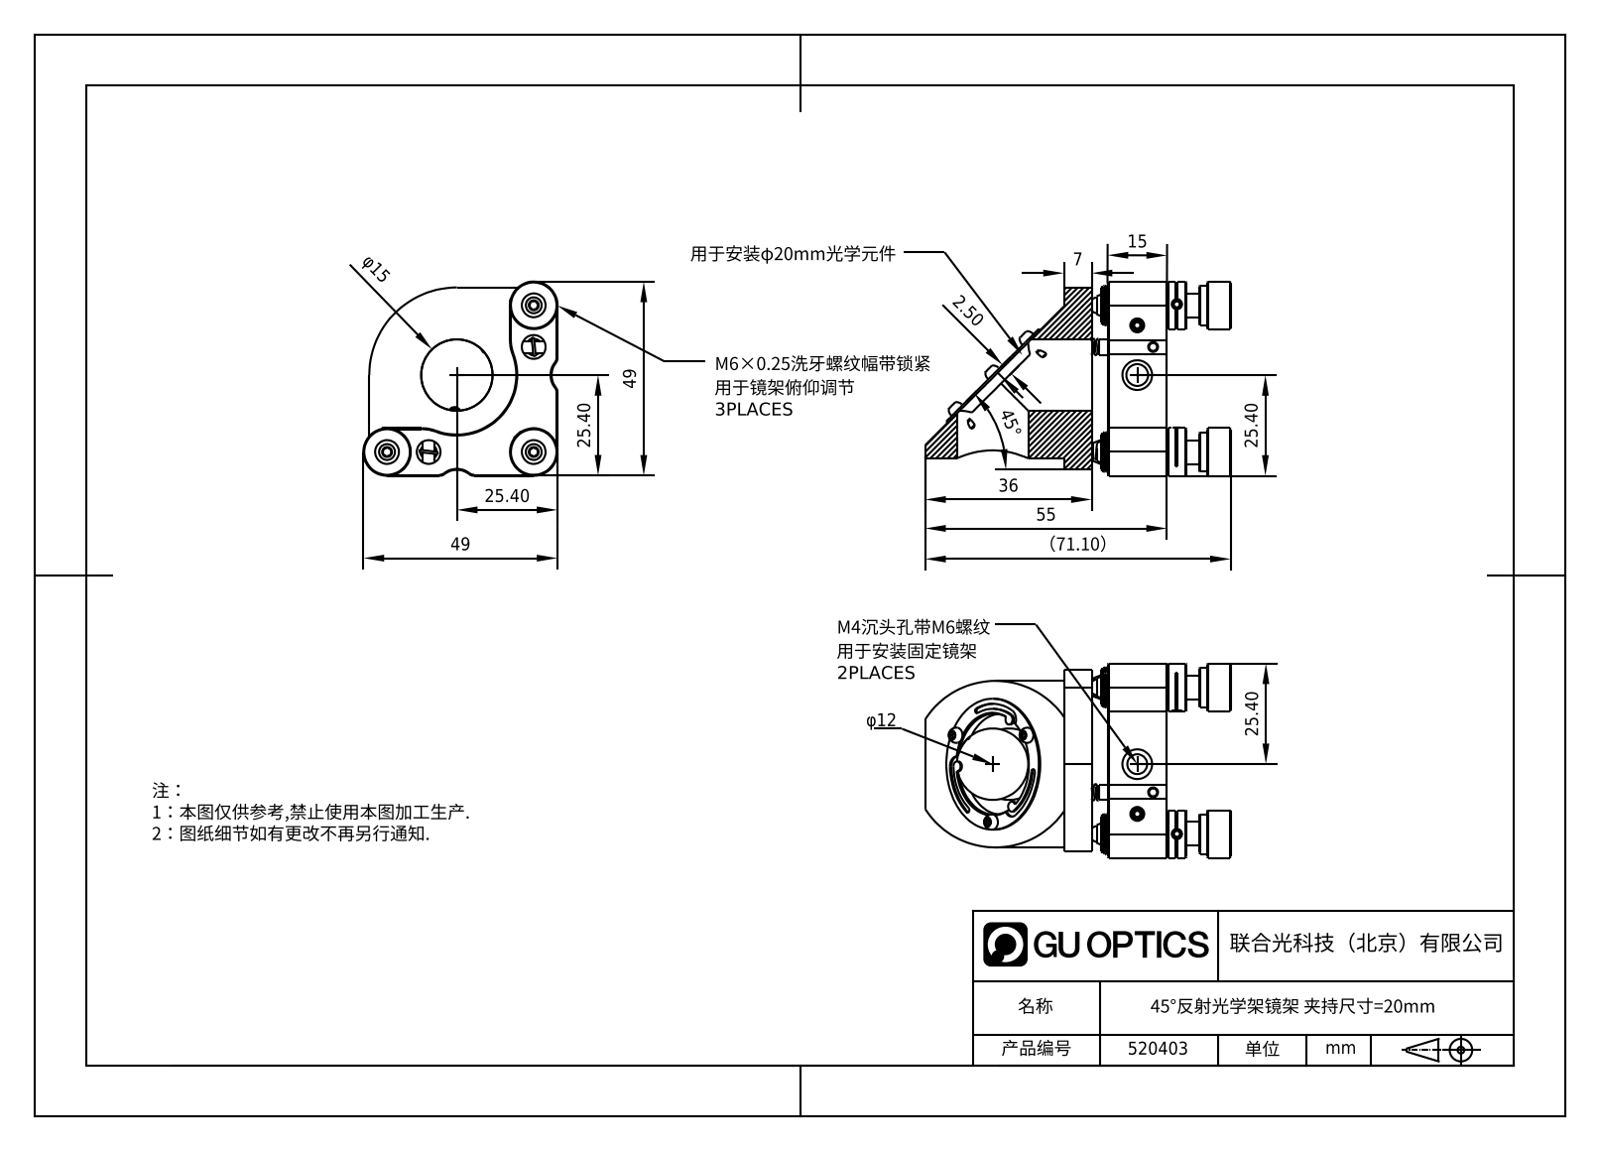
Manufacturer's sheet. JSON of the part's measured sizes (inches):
{"part_name": "520403", "step_written_by": "SolidWorks 2020 (CONFIG_CONTROL_DESIGN)", "units": "inches", "bodies": {"solids": 0, "faces": 390, "planar": 169, "cylindrical": 106, "other": 115}, "overall_size": [2.799, 1.929, 1.929], "round_holes": [[0.098, 4], [0.063, 3], [0.157, 3], [0.236, 2], [0.295, 2], [0.197, 1], [0.217, 1], [0.472, 1], [0.591, 1], [0.787, 1], [1.102, 1]], "round_bosses_or_shafts": [[0.118, 7], [0.472, 3], [0.394, 3], [0.374, 3], [0.315, 3], [0.236, 3], [0.083, 3], [0.157, 2]], "partial_cylinders_radius": [[0.008, 8], [0.079, 7], [0.02, 3], [0.039, 3], [0.177, 3], [0.031, 2], [0.197, 2], [0.394, 2]], "face_to_face_distances": [0.276, 1.024, 0.748, 0.433, 0.591, 0.157, 0.059, 0.02, 0.089, 0.108], "hole_center_spacings": [0.472, 0.321, 0.413, 0.643, 0.736, 0.813, 0.819, 1.031]}
